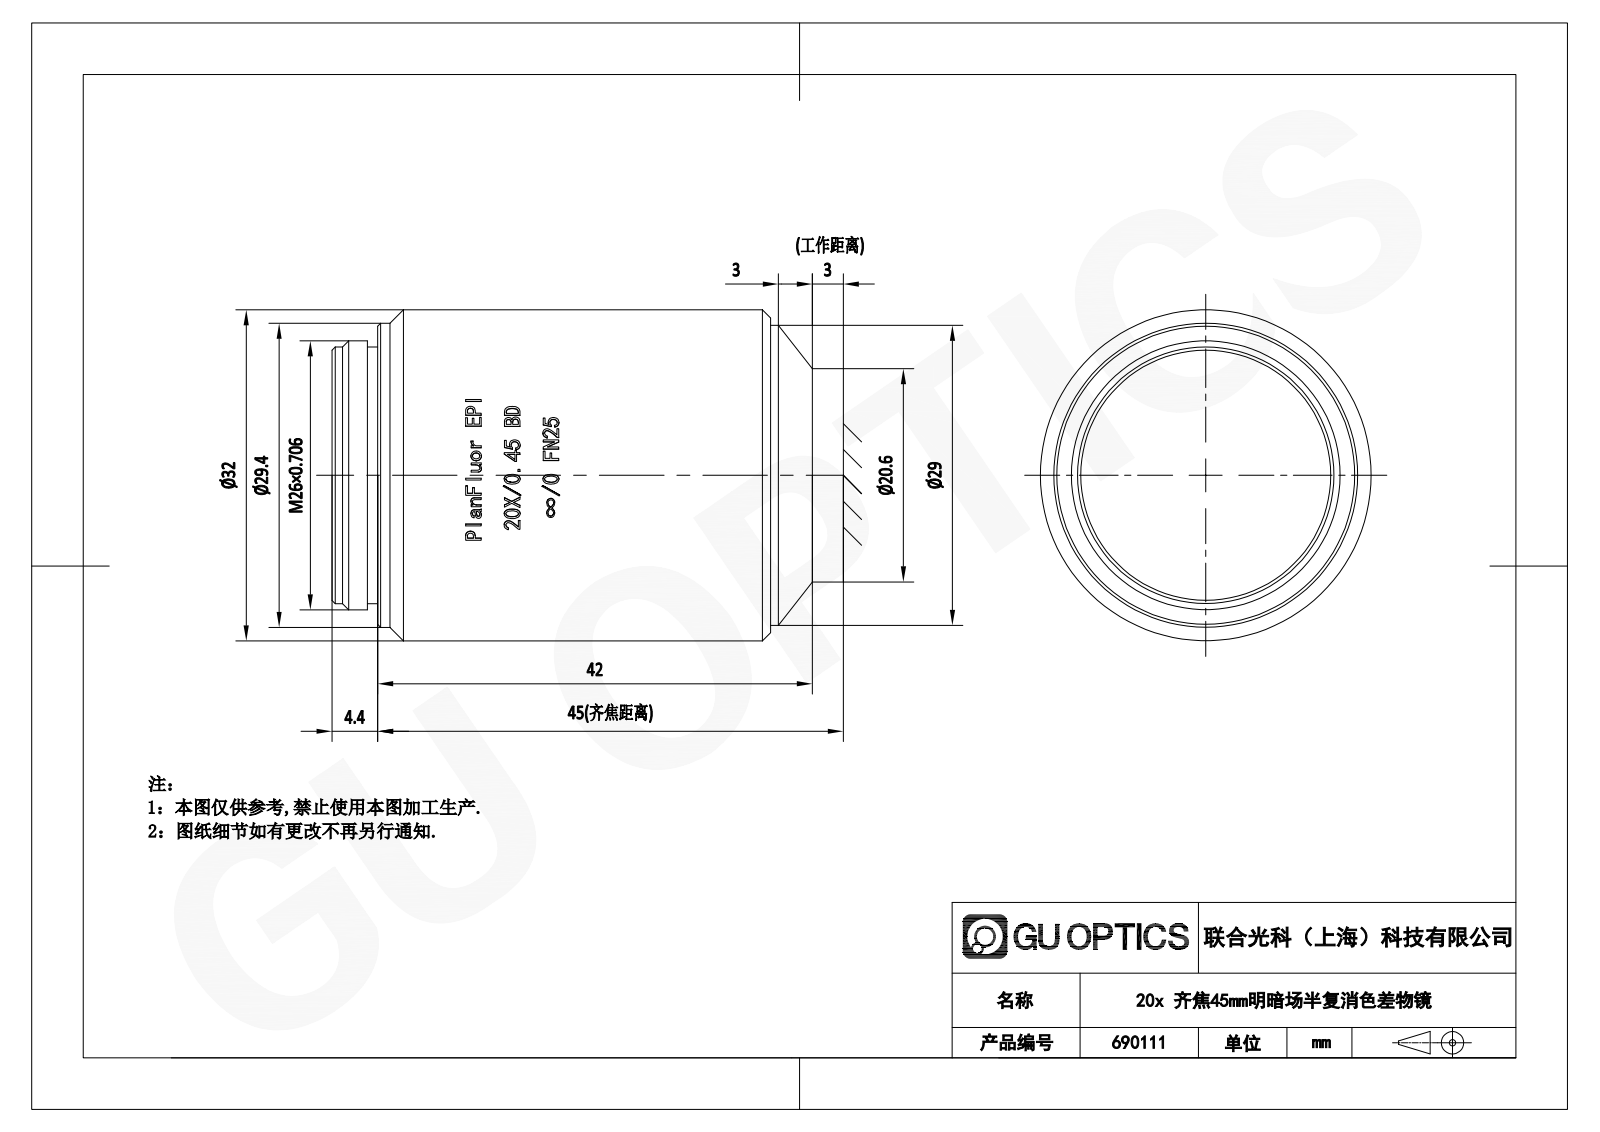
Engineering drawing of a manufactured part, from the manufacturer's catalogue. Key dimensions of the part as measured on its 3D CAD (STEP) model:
Part name (STEP PRODUCT): 690111
STEP written by: SolidWorks 2020 (CONFIG_CONTROL_DESIGN)
Units: millimetres
Bodies: 1 solid, 347 faces (154 planar, 54 cylindrical, 139 other)
Overall size (bounding box): 46.42 × 32.05 × 32
Volume: 34 604 mm³ · Surface area: 5 844 mm²
Round bosses / shafts (diameter × count): ⌀32 ×1, ⌀29.4 ×1, ⌀29 ×1, ⌀26 ×1, ⌀24.8 ×1
Partial cylindrical surfaces — rounded edges, fillets, slot ends (radius × count): R16.05 ×1
Main face-to-face distances: 46.42, 4.4, 42.02, 42.4, 38, 4.02, 3.4, 1, 39, 43.02
